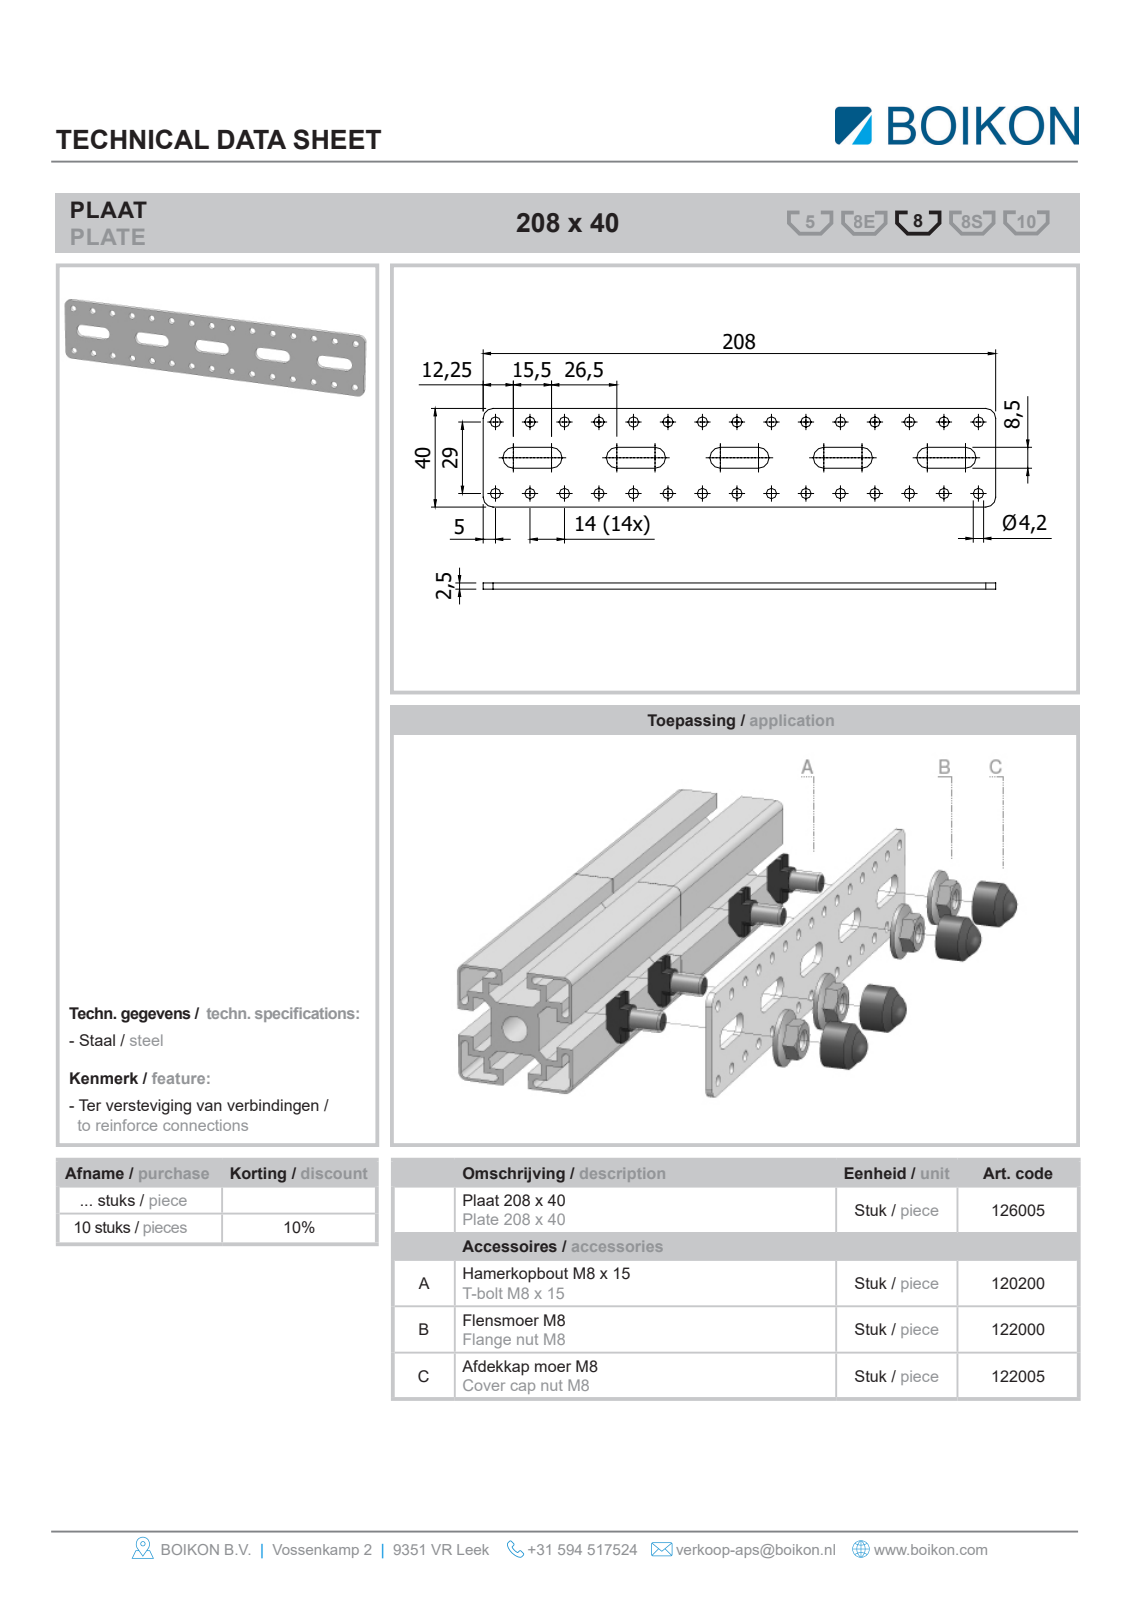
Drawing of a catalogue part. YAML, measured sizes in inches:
part_name: "Root; 126005 Hoekplaat 208 x 40BOIKON; 122000Flensmoer M8BOIKON; 122005Afdekkap voor moer M8BOIKON (+1 more)"
step_written_by: "HiCAD 2013 1802.4 Build 509 (AUTOMOTIVE_DESIGN)"
units: inches
bodies: {solids: 13, faces: 444, planar: 292, cylindrical: 100, other: 52}
overall_size: [8.189, 1.575, 1.189]
volume: 2.175
surface_area: 46.38
round_holes:
  - {diameter: 0.165, count: 30}
  - {diameter: 0.315, count: 4}
round_bosses_or_shafts:
  - {diameter: 0.827, count: 4}
  - {diameter: 0.661, count: 4}
  - {diameter: 0.255, count: 4}
partial_cylinders:
  - {radius: 0.039, count: 16}
  - {radius: 0.167, count: 10}
  - {radius: 0.016, count: 8}
  - {radius: 0.157, count: 4}
  - {radius: 0.197, count: 4}
  - {radius: 0.382, count: 4}
face_to_face_distances: [0.098, 0.512, 0.335, 0.374, 0.276, 0.531, 1.043, 0.62, 0.955, 1.575]
hole_center_spacings: [0.551, 1.102, 1.654, 1.268, 1.587, 2.009, 2.205, 2.483]
